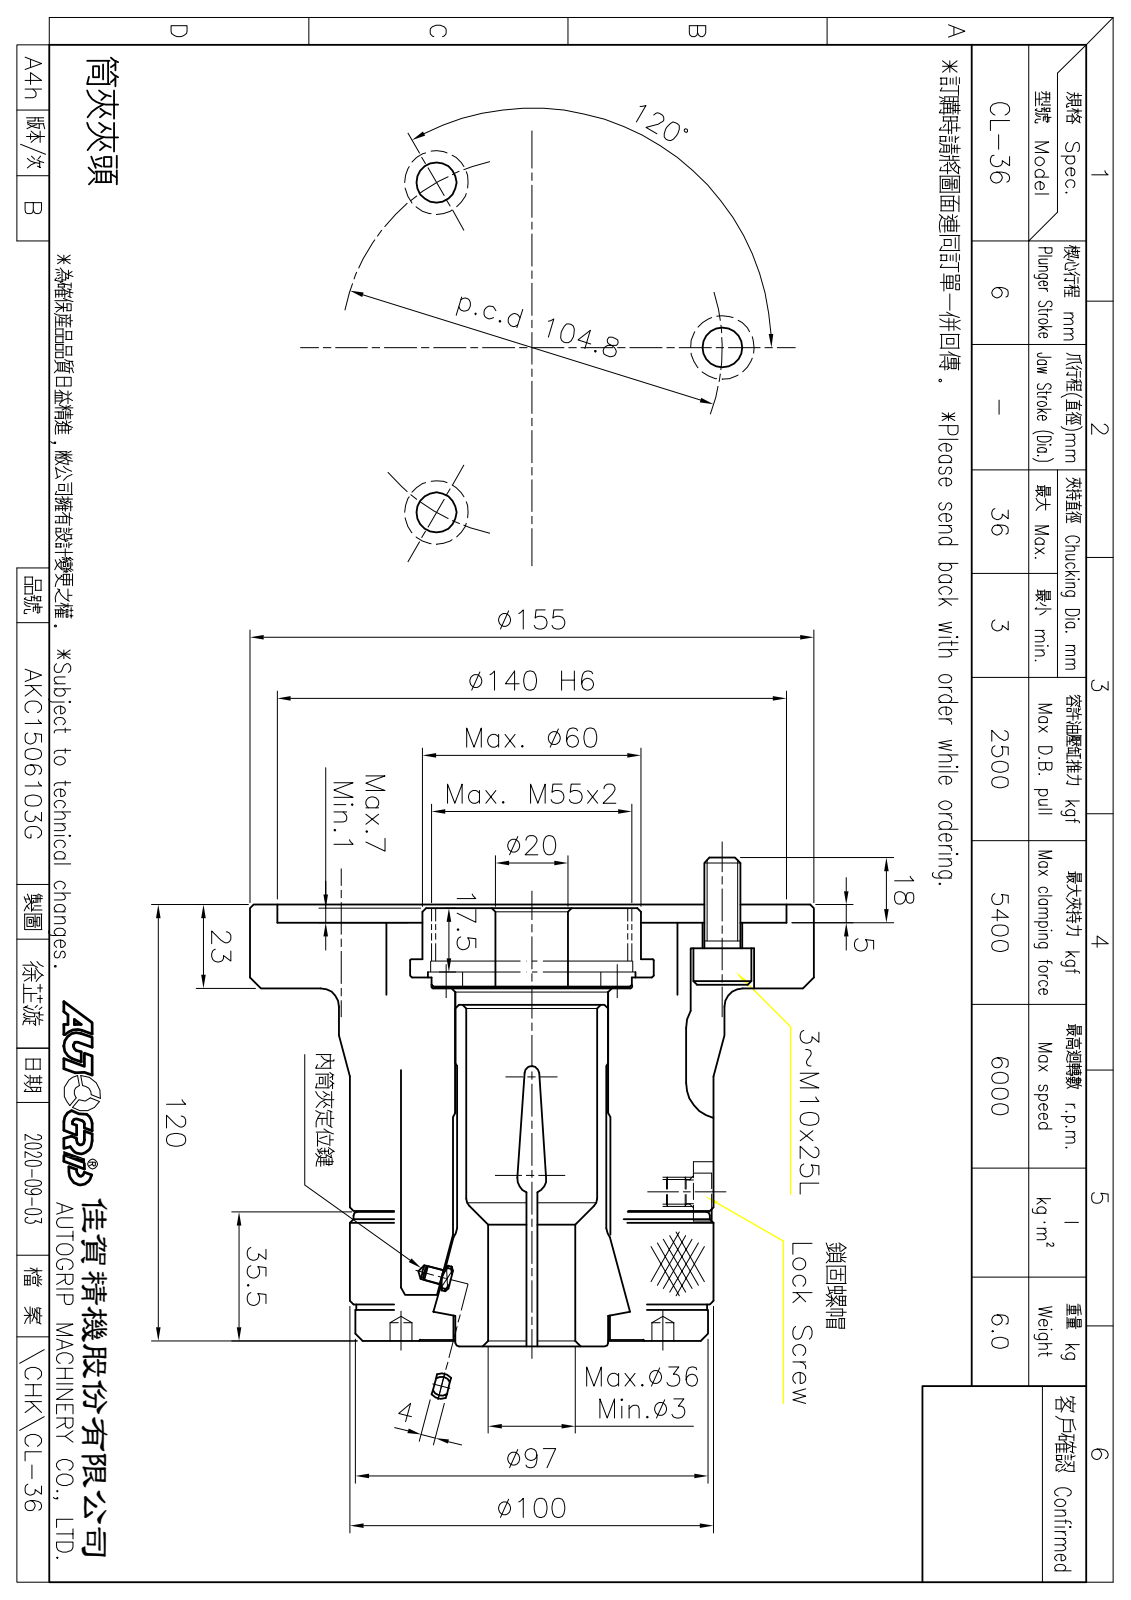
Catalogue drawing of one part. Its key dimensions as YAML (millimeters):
part_name: "CF-CL-36-03010; 圓頭內六角螺栓_M10x25; FSW320300; CF-CL-42-01020 (+4 more)"
step_written_by: "SolidWorks 2020 (CONFIG_CONTROL_DESIGN)"
units: millimeters
bodies: {solids: 9, faces: 223, planar: 94, cylindrical: 60, other: 69}
overall_size: [155, 155, 133]
volume: 910071
surface_area: 188703
round_holes:
  - {diameter: 5, count: 3}
  - {diameter: 11, count: 3}
  - {diameter: 17.5, count: 3}
  - {diameter: 6, count: 2}
  - {diameter: 4, count: 1}
  - {diameter: 6.8, count: 1}
  - {diameter: 38, count: 1}
  - {diameter: 42, count: 1}
  - {diameter: 43, count: 1}
  - {diameter: 43.3, count: 1}
  - {diameter: 53, count: 1}
  - {diameter: 55, count: 1}
round_bosses_or_shafts:
  - {diameter: 16, count: 3}
  - {diameter: 10, count: 3}
  - {diameter: 155, count: 1}
  - {diameter: 106, count: 1}
  - {diameter: 100, count: 1}
  - {diameter: 98, count: 1}
  - {diameter: 97, count: 1}
  - {diameter: 96.4, count: 1}
partial_cylinders:
  - {radius: 8.5, count: 3}
  - {radius: 10, count: 3}
  - {radius: 3.5, count: 1}
  - {radius: 8, count: 1}
  - {radius: 8.25, count: 1}
face_to_face_distances: [18, 2.79, 115, 97, 5, 23.21, 9.5, 11, 15.21, 99.79]
hole_center_spacings: [15.44, 52.4, 58, 87.65, 90.76, 100.45, 102.02, 27.83]
